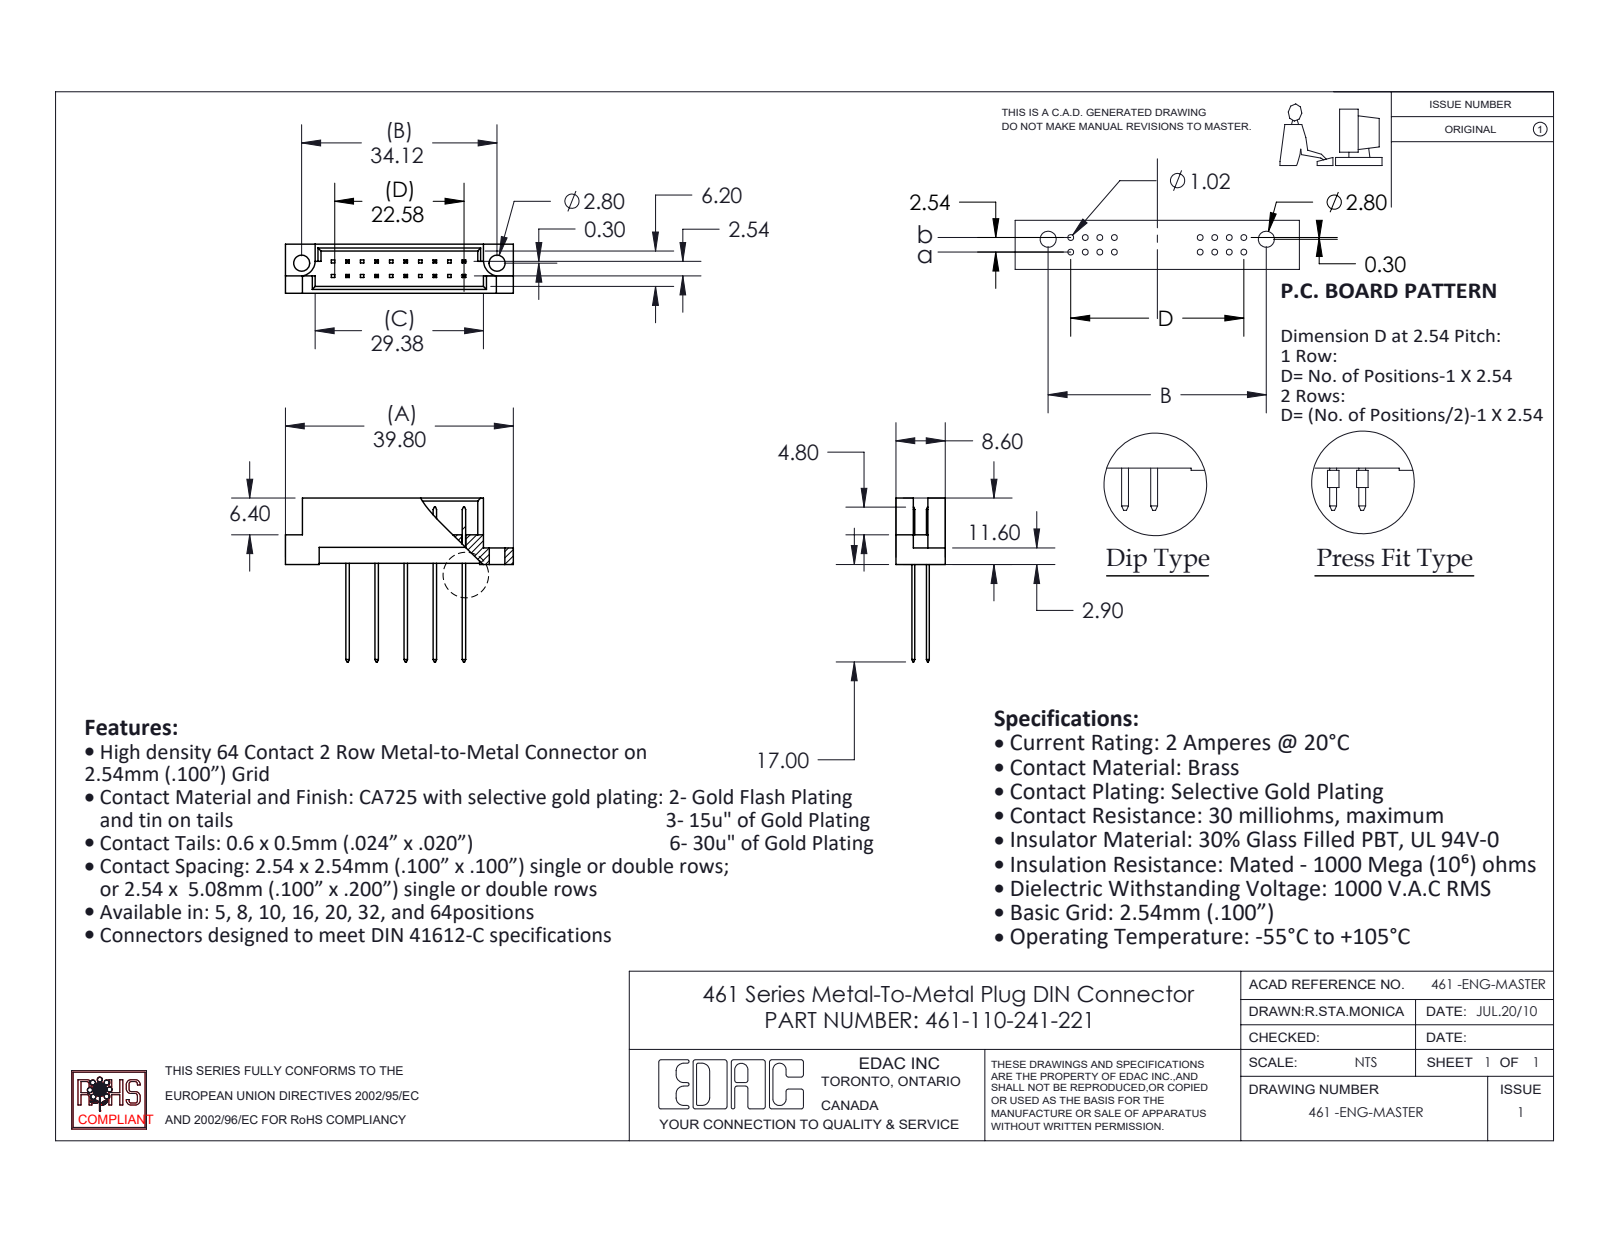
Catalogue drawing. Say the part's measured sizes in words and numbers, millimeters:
The part is named "461 Part_20; 461-110-241-221; 461-290_41". Its 3-D file was written by "SolidWorks 2020 (CONFIG_CONTROL_DESIGN)". It is 11 solids with 268 faces: 262 planar, 6 cylindrical and 0 other. Overall it measures 39.8 by 28.6 by 8.6 millimeters. Its volume is 1 985 cubic millimeters and its surface area 2 928 square millimeters. Round holes: 2 of diameter 2.8. Partial cylindrical surfaces (rounded edges, fillets, slot ends): 2 of radius 2.8. The main face-to-face distances are 1.2, 7.4, 8.6, 5.08, 6.2, 2.54, 3.28, 5.32, 2.08, 4.12. The hole center spacings are 34.12.
